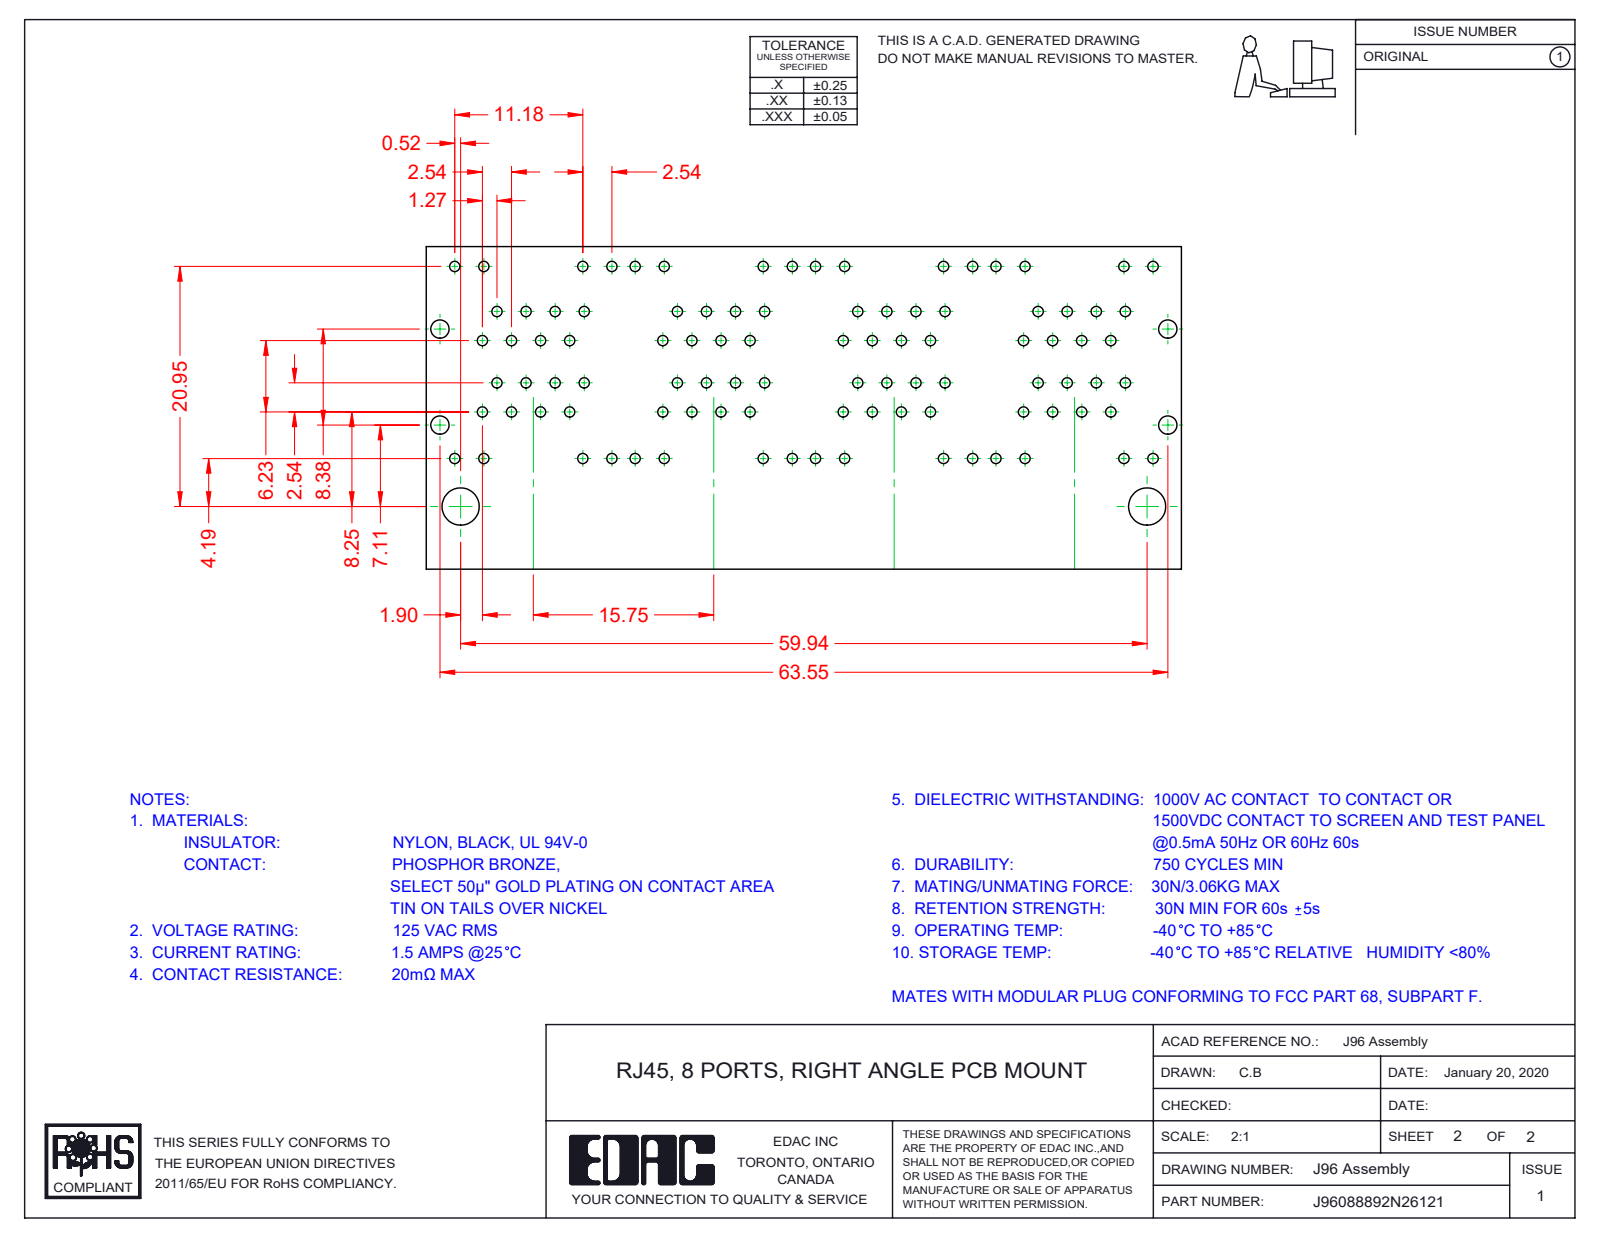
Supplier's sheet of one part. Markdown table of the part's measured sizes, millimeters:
| quantity | value |
| --- | --- |
| part name | 96 LED RH Upper_6-Red-Green; 96 Grounding_8 Ports; 96 LED LH Upper_2-Red; 96 Contact Lock Lower (+8 more) |
| STEP written by | SolidWorks 2016 (CONFIG_CONTROL_DESIGN) |
| units | millimeters |
| bodies | 96 solids, 7658 faces (6069 planar, 1323 cylindrical, 266 other) |
| overall size | 64.05 × 29.58 × 28.68 |
| volume | 24 160 mm³ |
| surface area | 63 658 mm² |
| round holes (diameter × count) | 1.7 × 3 |
| round bosses / shafts (diameter × count) | 1.68 × 3 |
| partial cylindrical surfaces (radius × count) | 0.25 × 124, 0.35 × 73, 1 × 72, 0.5 × 49, 0.91 × 32, 0.2 × 21, 0.7 × 11, 0.22 × 8 |
| main face-to-face distances | 15.75, 0.35, 9.95, 1.17, 1.6, 0.54, 9.98, 10.18, 12.67, 3.37 |
| hole center spacings | 15.75, 31.5 |
